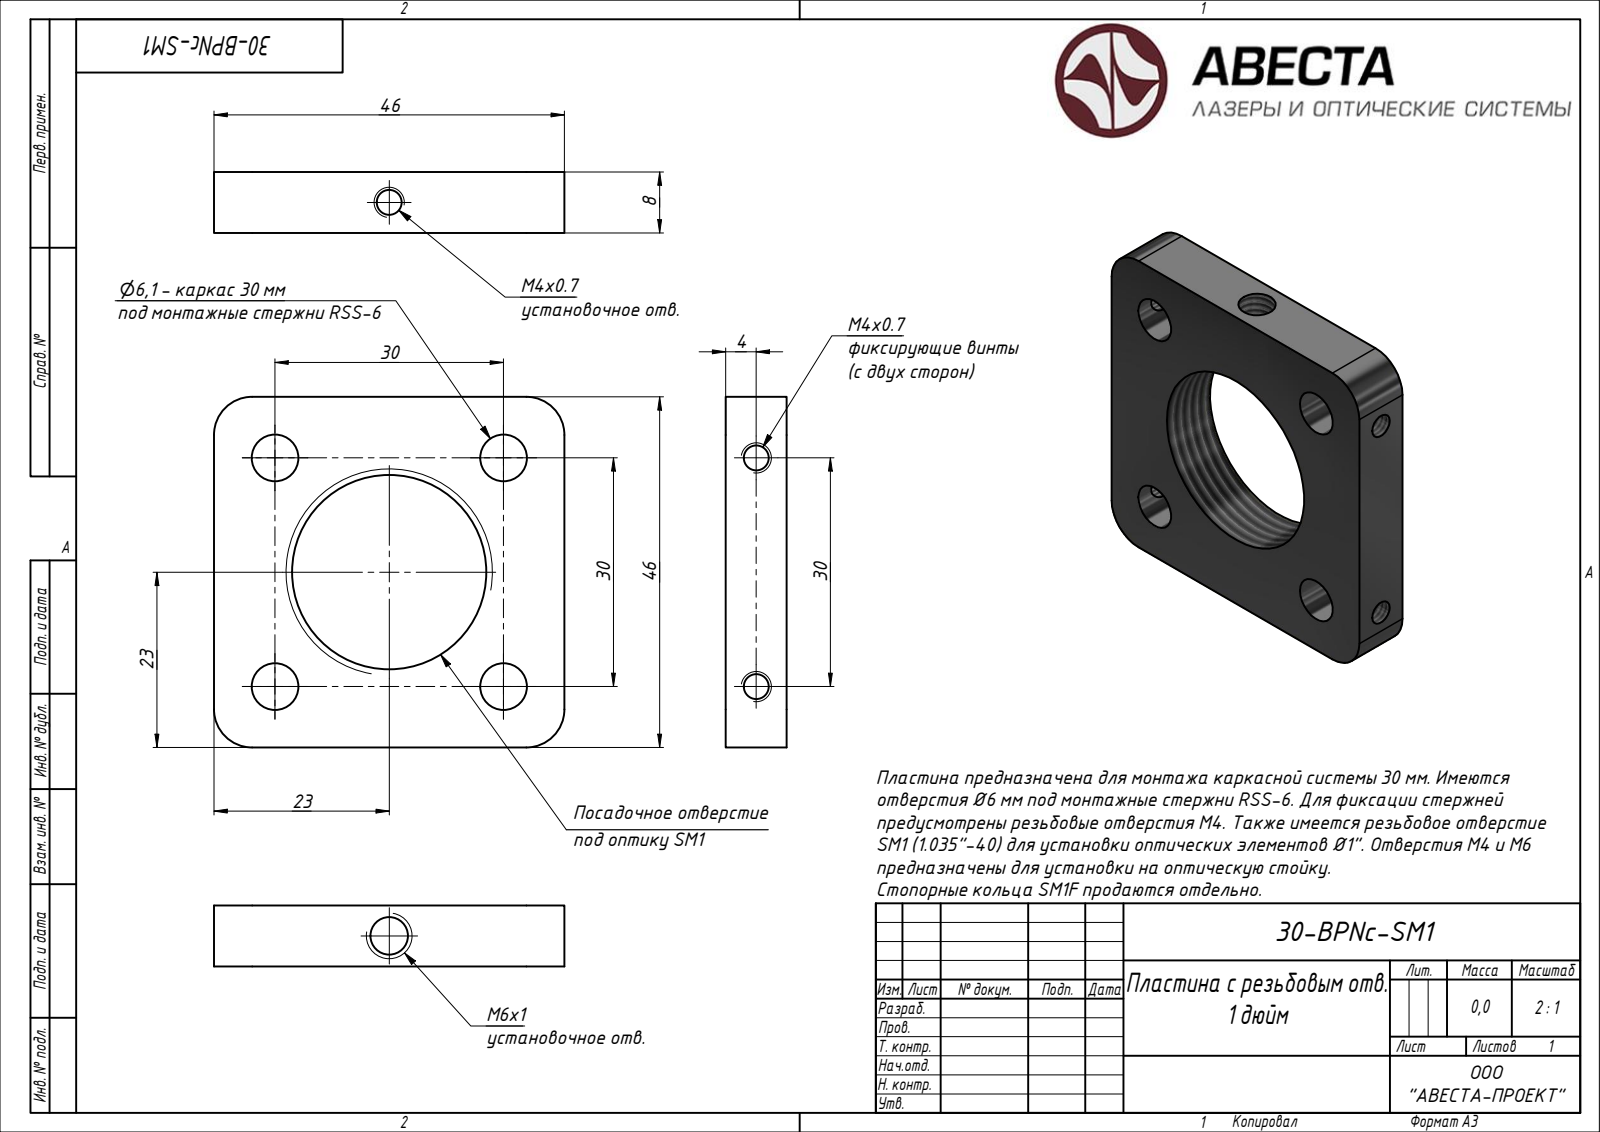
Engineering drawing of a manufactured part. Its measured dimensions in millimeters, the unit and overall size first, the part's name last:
Units: millimetres
Overall size (bounding box): 46 × 46 × 8
Round holes (diameter × count): ⌀6.1 ×4, ⌀3.24 ×3, ⌀4.92 ×1, ⌀25.48 ×1
Partial cylindrical surfaces — rounded edges, fillets, slot ends (radius × count): R5 ×4
Main face-to-face distances: 8, 46, 6, 40
Hole centre spacings: 30, 21.21, 42.43
Volume: 11 402 mm³ · Surface area: 5 893 mm²
Bodies: 1 solid, 23 faces (7 planar, 15 cylindrical, 1 other)
Part name (STEP PRODUCT): 30-BPNc-SM1
STEP written by: Autodesk Inventor 2020 (AUTOMOTIVE_DESIGN)
